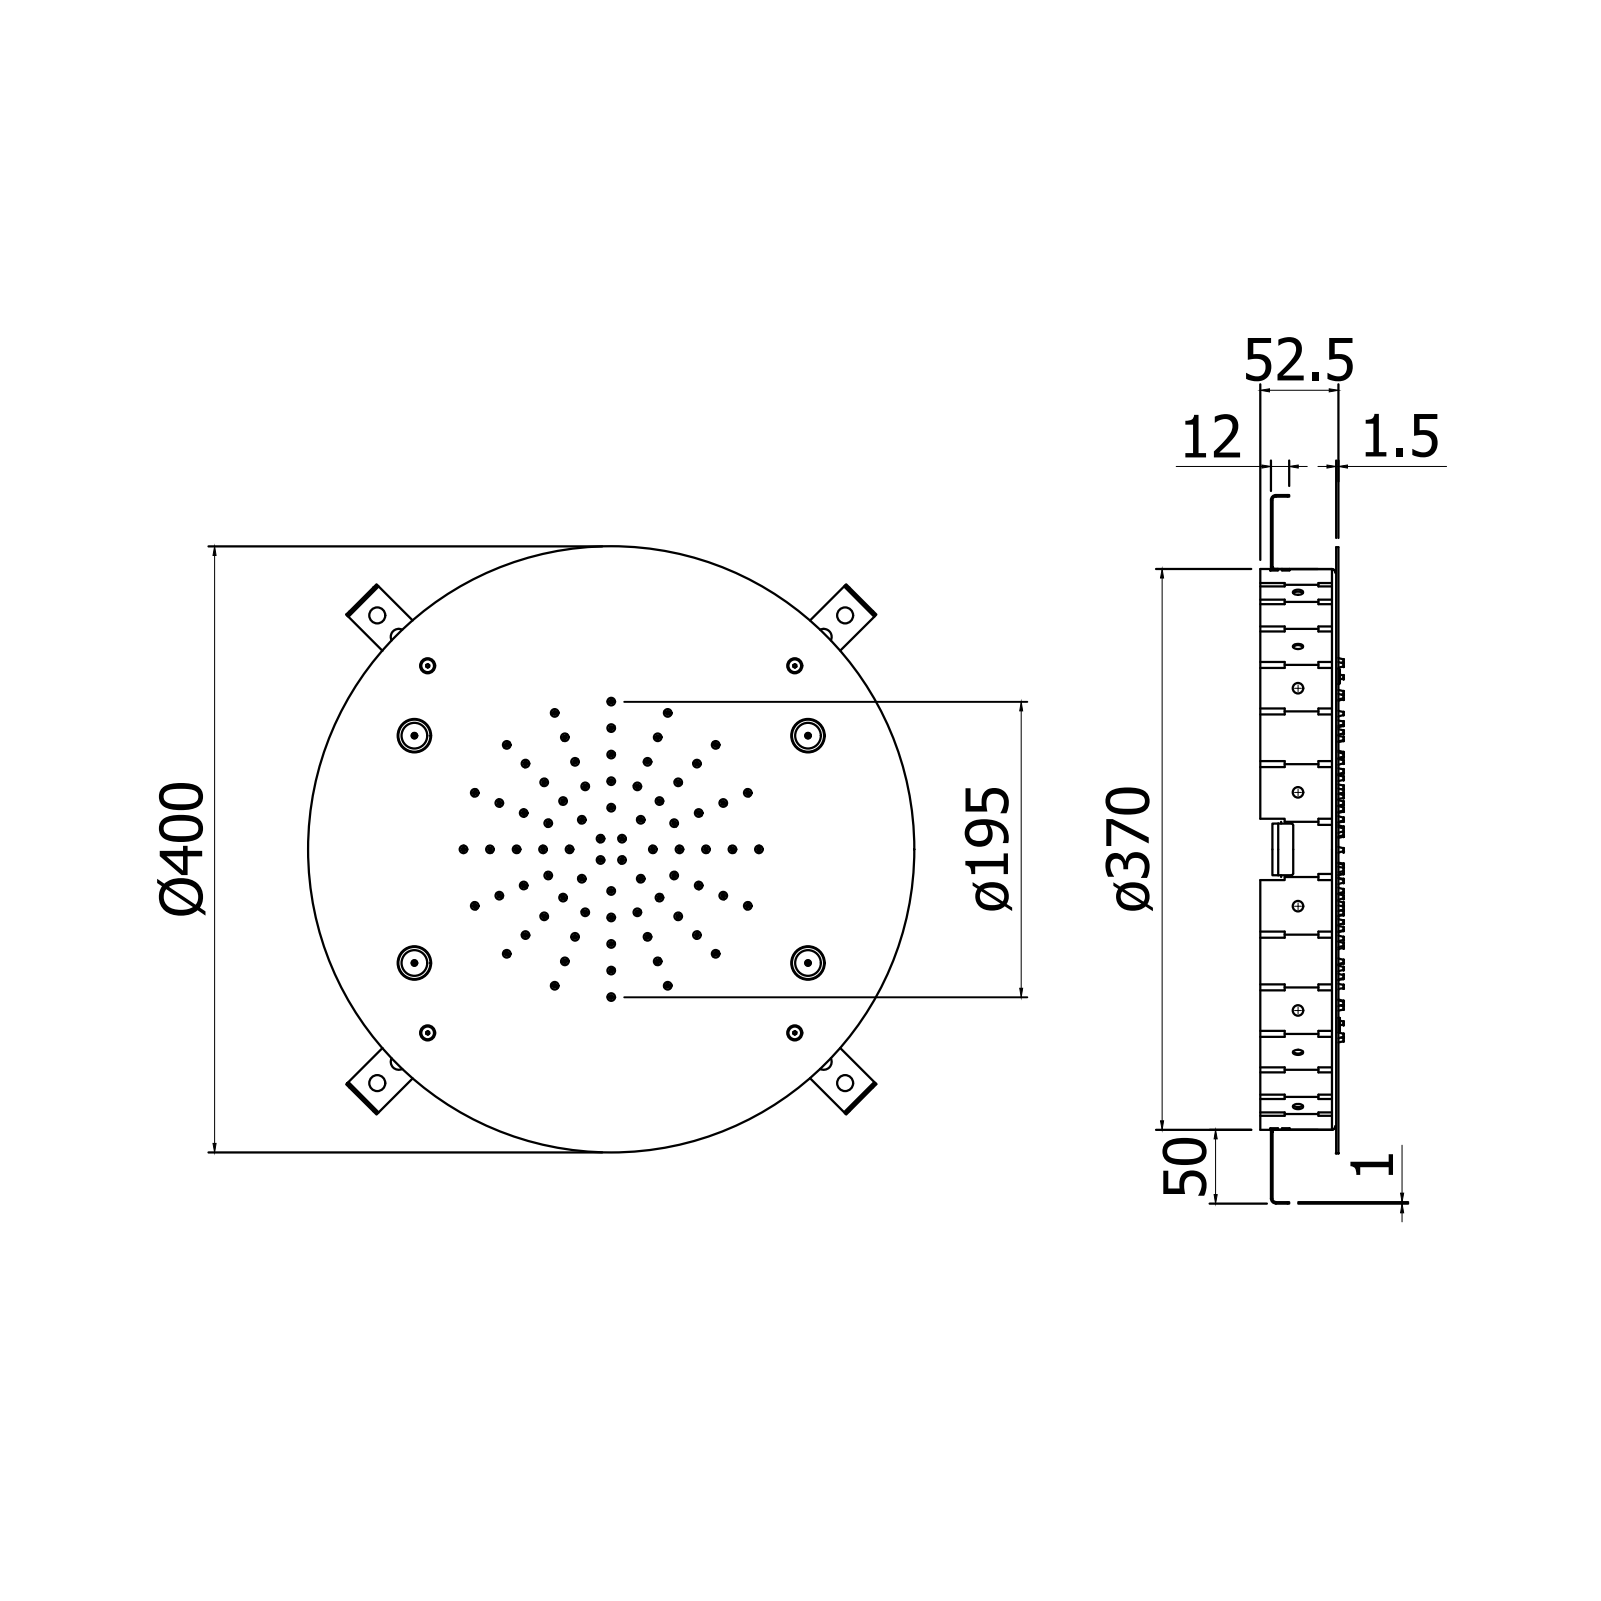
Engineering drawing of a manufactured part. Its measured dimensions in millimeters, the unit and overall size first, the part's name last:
Units: millimetres
Overall size (bounding box): 400 × 400 × 4.8
Round holes (diameter × count): ⌀1.5 ×80, ⌀5 ×76, ⌀7 ×4, ⌀17.05 ×4
Round bosses / shafts (diameter × count): ⌀20 ×4, ⌀16.65 ×4, ⌀10 ×4, ⌀5 ×4, ⌀400 ×1
Partial cylindrical surfaces — rounded edges, fillets, slot ends (radius × count): R0.2 ×24
Main face-to-face distances: 1.5, 1, 2.5, 2.3, 3.3, 4.8, 2, 65.4, 258.48, 2.01
Hole centre spacings: 21.05, 21.62, 29.27, 32.11, 35.29, 50.82, 52.74, 67.32
Volume: 190 206 mm³ · Surface area: 260 338 mm²
Bodies: 1 solid, 1320 faces (118 planar, 386 cylindrical, 816 other)
Part name (STEP PRODUCT): 4072033CR
STEP written by: CREO PARAMETRIC BY PTC INC, 2020044 (CONFIG_CONTROL_DESIGN)
